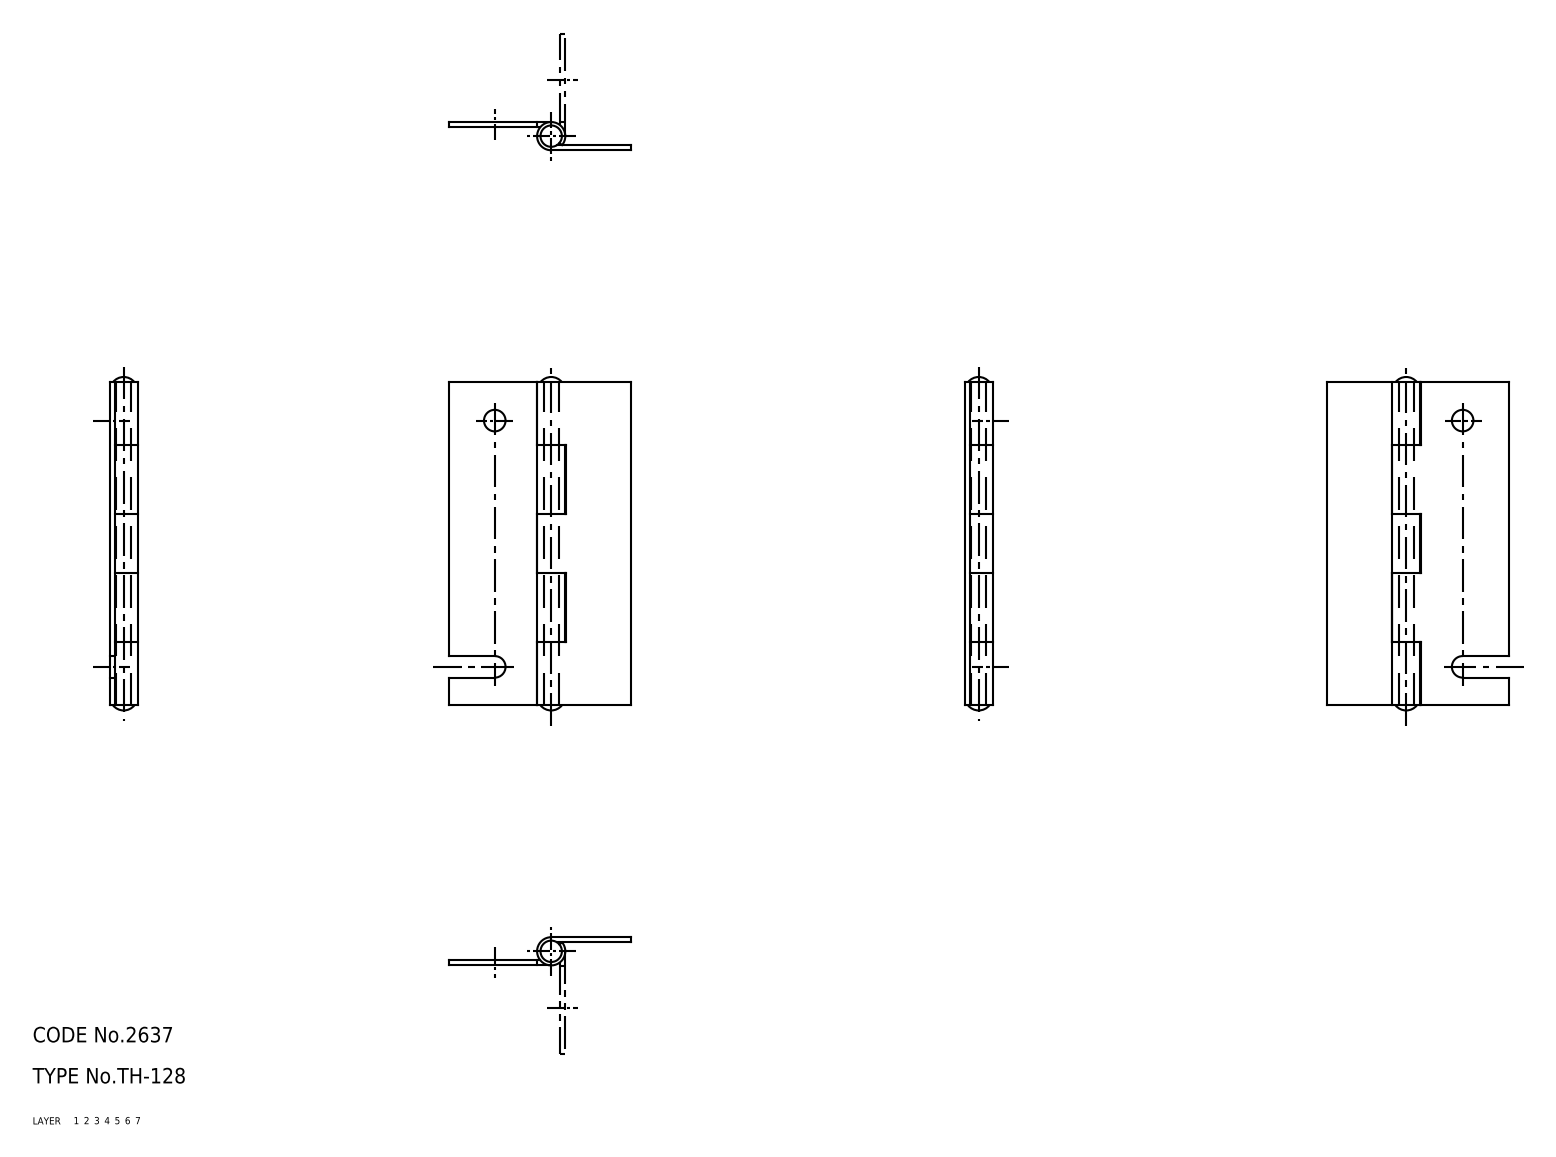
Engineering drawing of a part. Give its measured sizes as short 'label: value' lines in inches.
name: shaft; hinge piece_B; hinge piece_A; TH_128_3021_36
written by: CADfix (AUTOMOTIVE_DESIGN)
unit: in
bodies: 3 solids, 50 faces (0 planar, 0 cylindrical, 50 other)
size: 2.559 × 1.398 × 0.217
volume: 0.197 in³; area: 10.33 in²
